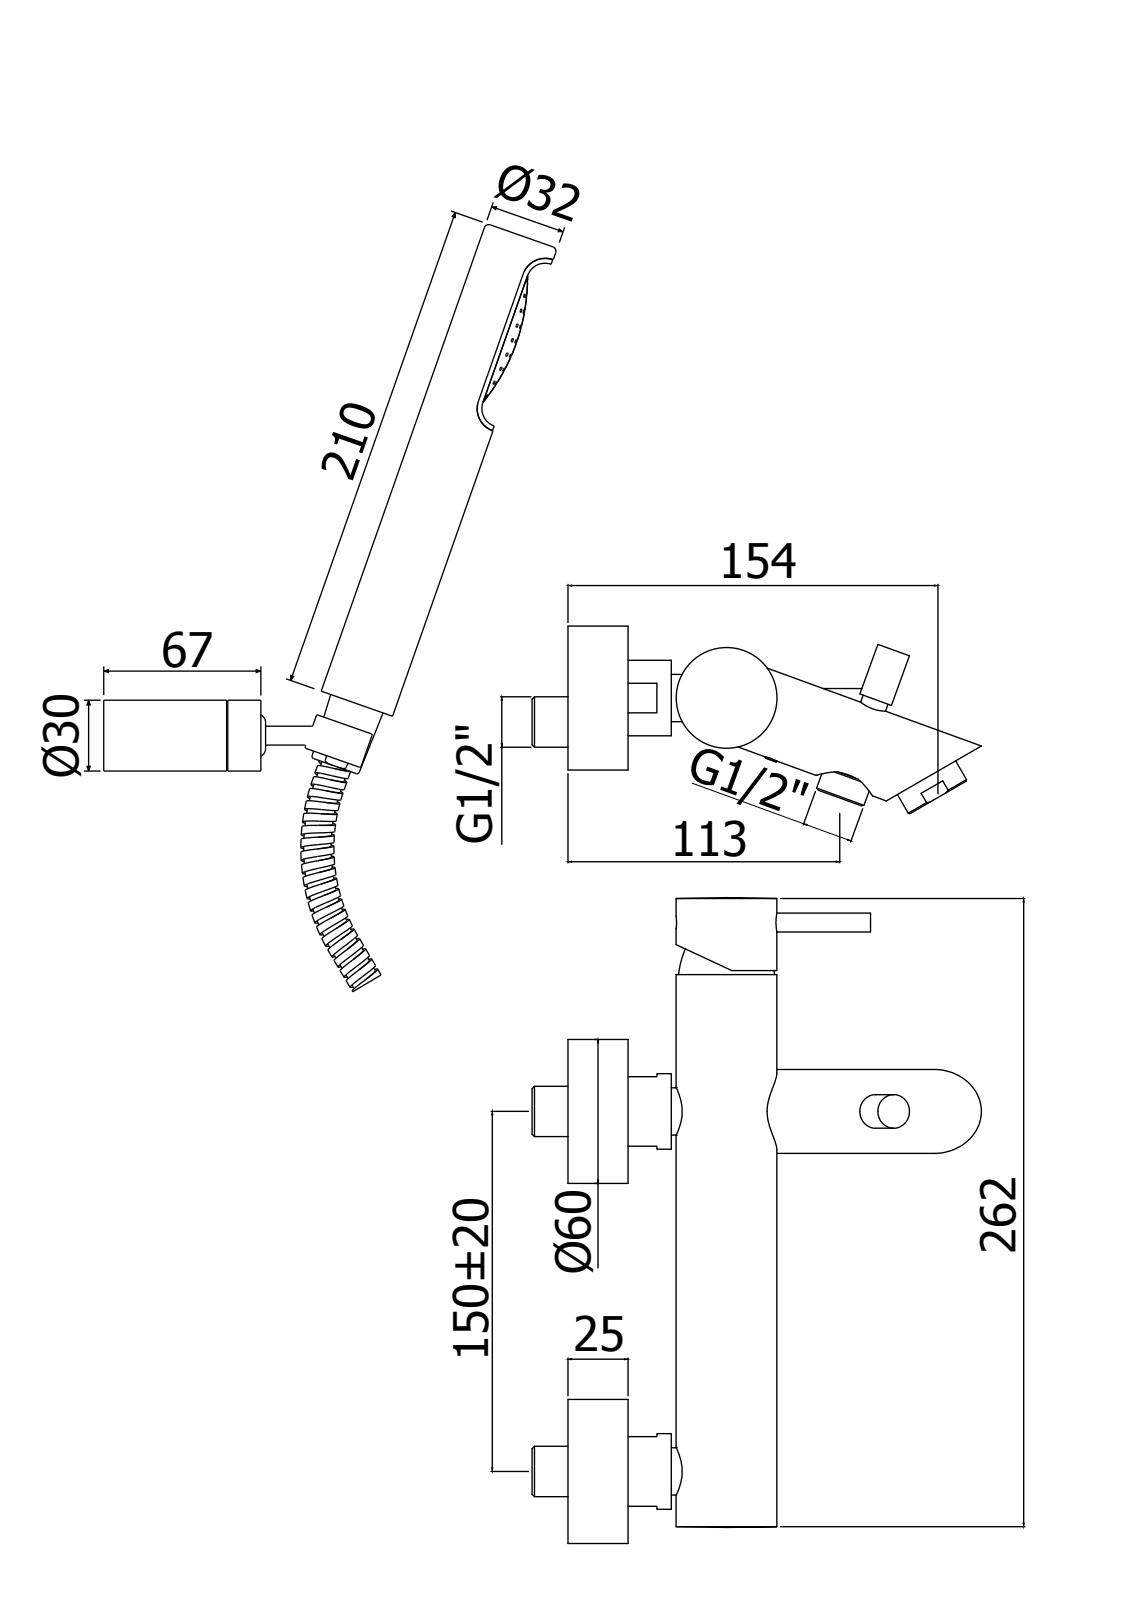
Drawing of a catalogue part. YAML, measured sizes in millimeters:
part_name: "BI023LCR"
step_written_by: "CREO PARAMETRIC BY PTC INC, 2020044 (CONFIG_CONTROL_DESIGN)"
units: millimeters
bodies: {solids: 5, faces: 2890, planar: 2020, cylindrical: 504, other: 366}
overall_size: [440.75, 314.44, 192.05]
volume: 530267
surface_area: 209738
round_holes:
  - {diameter: 1.5, count: 45}
  - {diameter: 5, count: 6}
  - {diameter: 7.5, count: 6}
  - {diameter: 12, count: 5}
  - {diameter: 8, count: 3}
  - {diameter: 9, count: 3}
  - {diameter: 16, count: 3}
  - {diameter: 18, count: 3}
  - {diameter: 24.5, count: 3}
  - {diameter: 4, count: 2}
  - {diameter: 10.5, count: 2}
  - {diameter: 16.7, count: 2}
round_bosses_or_shafts:
  - {diameter: 24, count: 3}
  - {diameter: 59.5, count: 2}
  - {diameter: 35, count: 2}
  - {diameter: 31.5, count: 2}
  - {diameter: 21, count: 2}
  - {diameter: 20.8, count: 2}
  - {diameter: 19.7, count: 2}
  - {diameter: 5, count: 2}
partial_cylinders:
  - {radius: 0.5, count: 54}
  - {radius: 0.15, count: 11}
  - {radius: 0.3, count: 9}
  - {radius: 1, count: 4}
  - {radius: 7, count: 4}
  - {radius: 4.5, count: 2}
  - {radius: 7.8, count: 2}
  - {radius: 7.95, count: 2}
face_to_face_distances: [4.7, 3, 2, 20, 24.7, 10, 1, 18, 12, 0.5]
hole_center_spacings: [7.91, 20.01, 6.5, 13, 26.38, 4.5, 11.1, 13.76]
